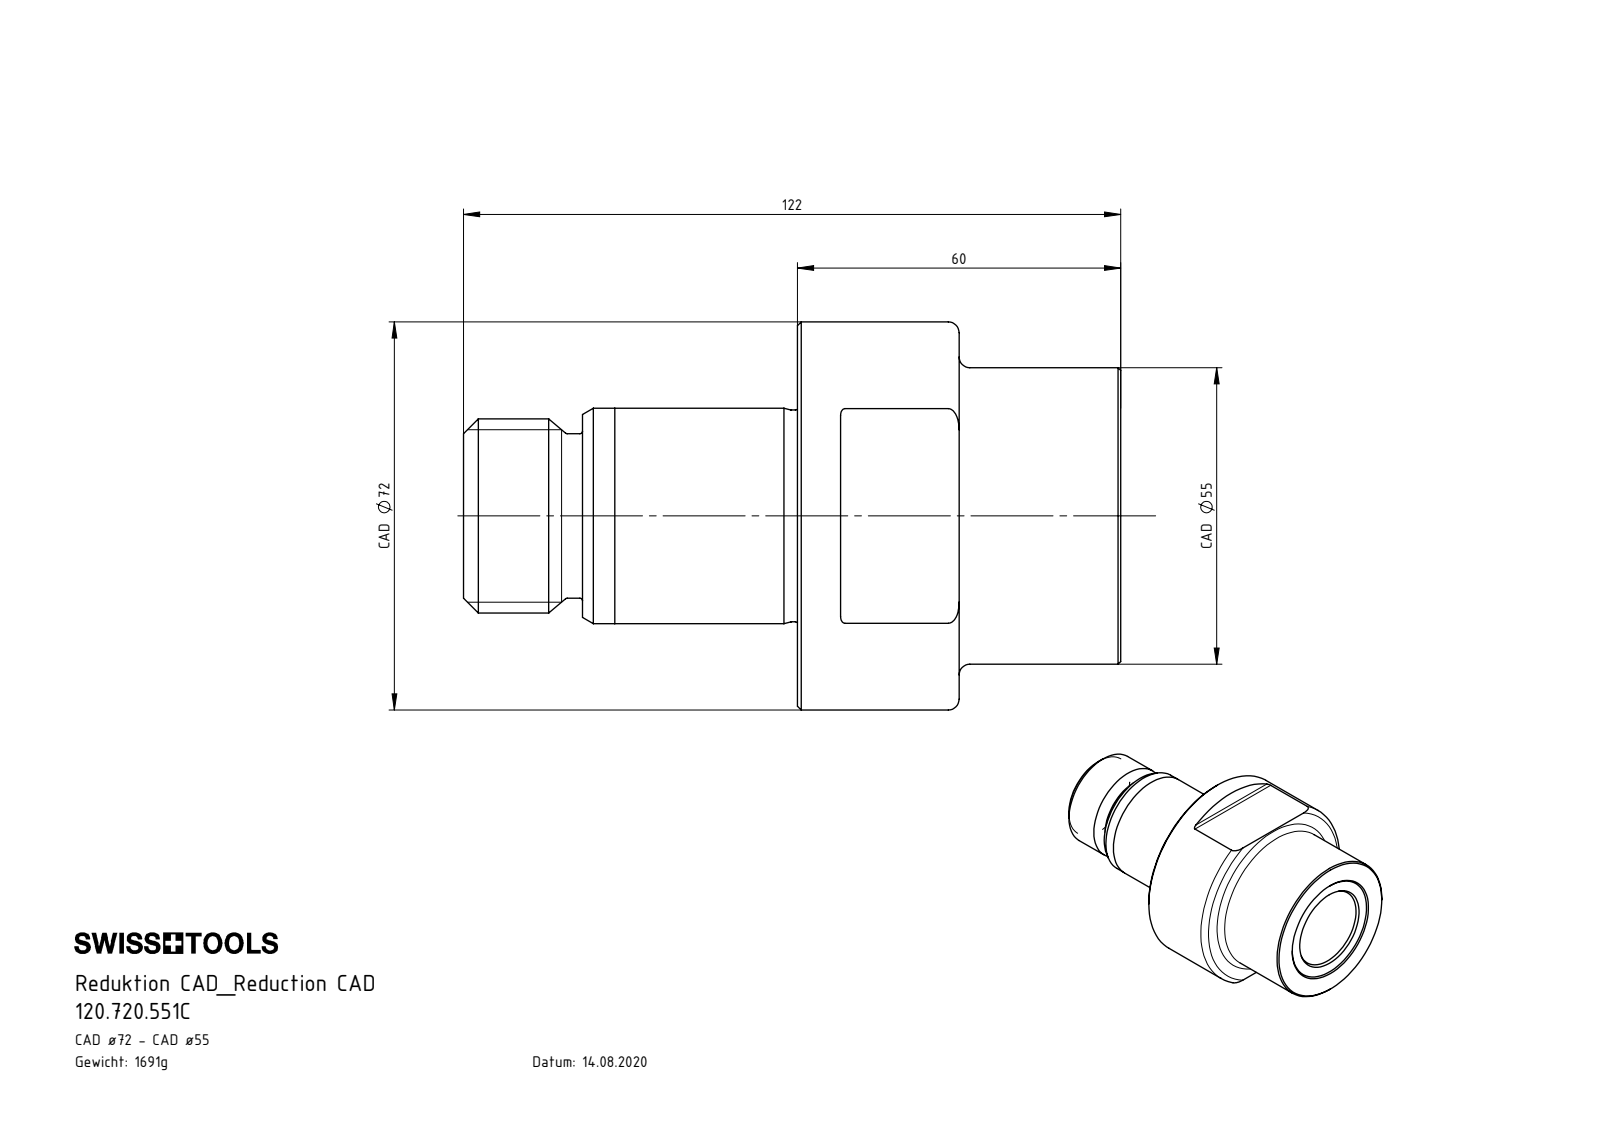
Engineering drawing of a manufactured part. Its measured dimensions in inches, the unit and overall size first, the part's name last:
Units: inches
Overall size (bounding box): 4.803 × 2.835 × 2.835
Round holes (diameter × count): ⌀0.335 ×1, ⌀0.965 ×1, ⌀1.181 ×1, ⌀1.205 ×1
Round bosses / shafts (diameter × count): ⌀2.835 ×1, ⌀2.165 ×1, ⌀1.575 ×1, ⌀1.573 ×1, ⌀1.547 ×1, ⌀1.417 ×1, ⌀1.201 ×1
Partial cylindrical surfaces — rounded edges, fillets, slot ends (radius × count): R0.031 ×2
Main face-to-face distances: 2.362, 1.181, 2.441, 3.622, 4.803, 1.161, 0.02, 4.783, 2.343, 0.87
Volume: 13.14 in³ · Surface area: 52.34 in²
Bodies: 1 solid, 79 faces (12 planar, 24 cylindrical, 43 other)
Part name (STEP PRODUCT): 120.720.551C
STEP written by: SolidWorks 2022 (CONFIG_CONTROL_DESIGN)
